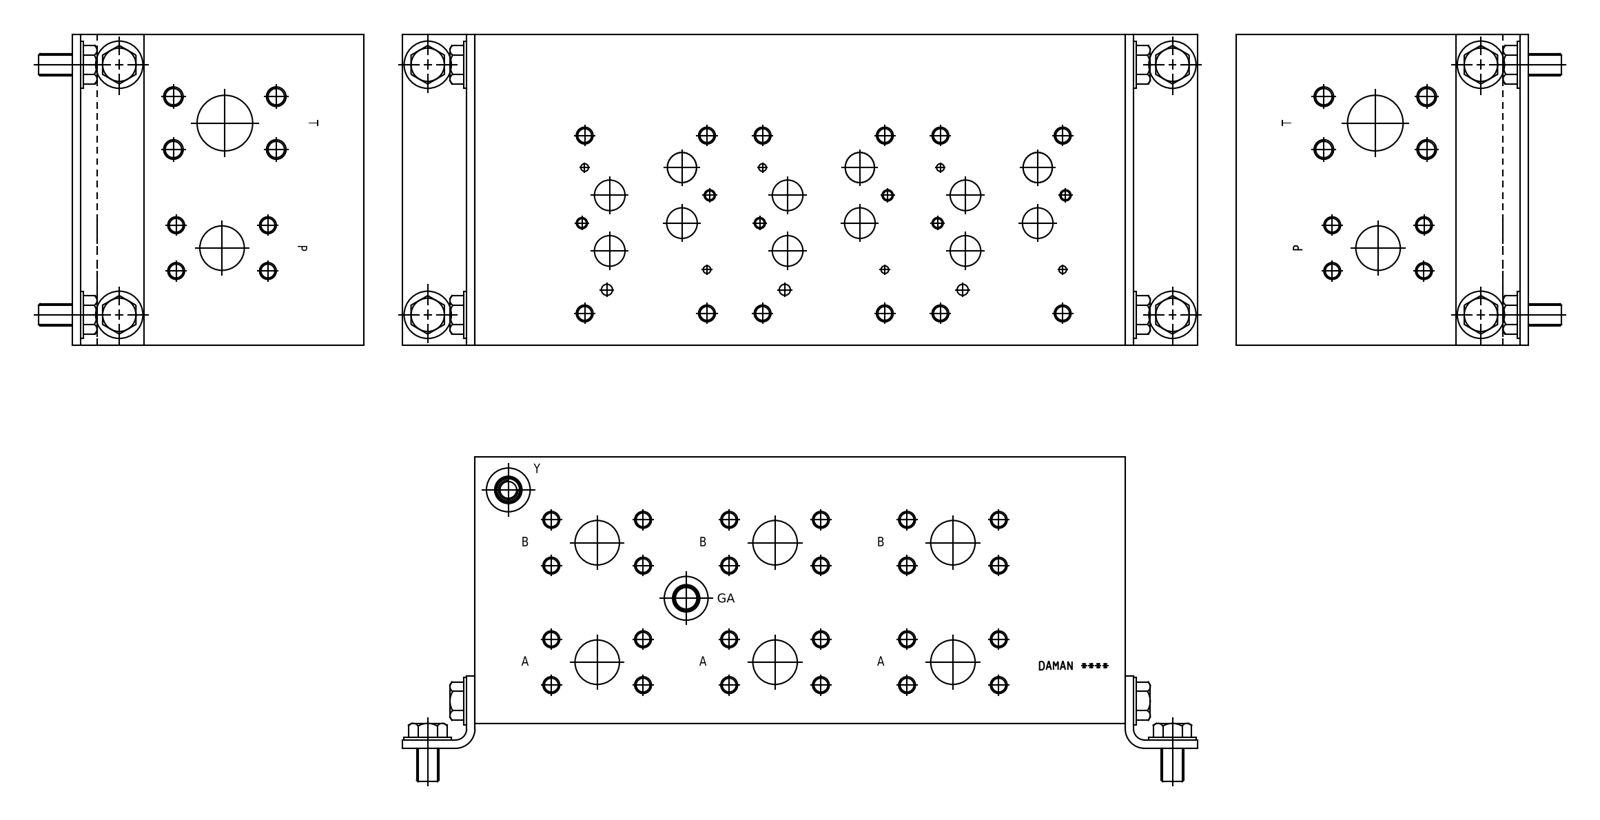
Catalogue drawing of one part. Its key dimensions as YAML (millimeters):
part_name: "Part_DD07HP034F_3D"
step_written_by: "Autodesk Inventor 2019 (AUTOMOTIVE_DESIGN)"
units: millimeters
bodies: {solids: 1, faces: 857, planar: 452, cylindrical: 165, other: 240}
overall_size: [371.48, 177.8, 152.4]
volume: 9848000
surface_area: 368113
round_holes:
  - {diameter: 9.53, count: 43}
  - {diameter: 7.92, count: 42}
  - {diameter: 6.35, count: 9}
  - {diameter: 17.48, count: 9}
  - {diameter: 25.4, count: 7}
  - {diameter: 4.37, count: 6}
  - {diameter: 5.11, count: 6}
  - {diameter: 9.35, count: 6}
  - {diameter: 11.13, count: 6}
  - {diameter: 16.66, count: 3}
  - {diameter: 10.72, count: 2}
  - {diameter: 12.7, count: 2}
face_to_face_distances: [152.4, 177.8, 371.48, 25.4, 0.79, 177.01, 24.61, 1, 127, 24.4]
hole_center_spacings: [101.6, 122.4, 203.2, 26.17, 104.92, 52.38, 58.55, 68.25]
